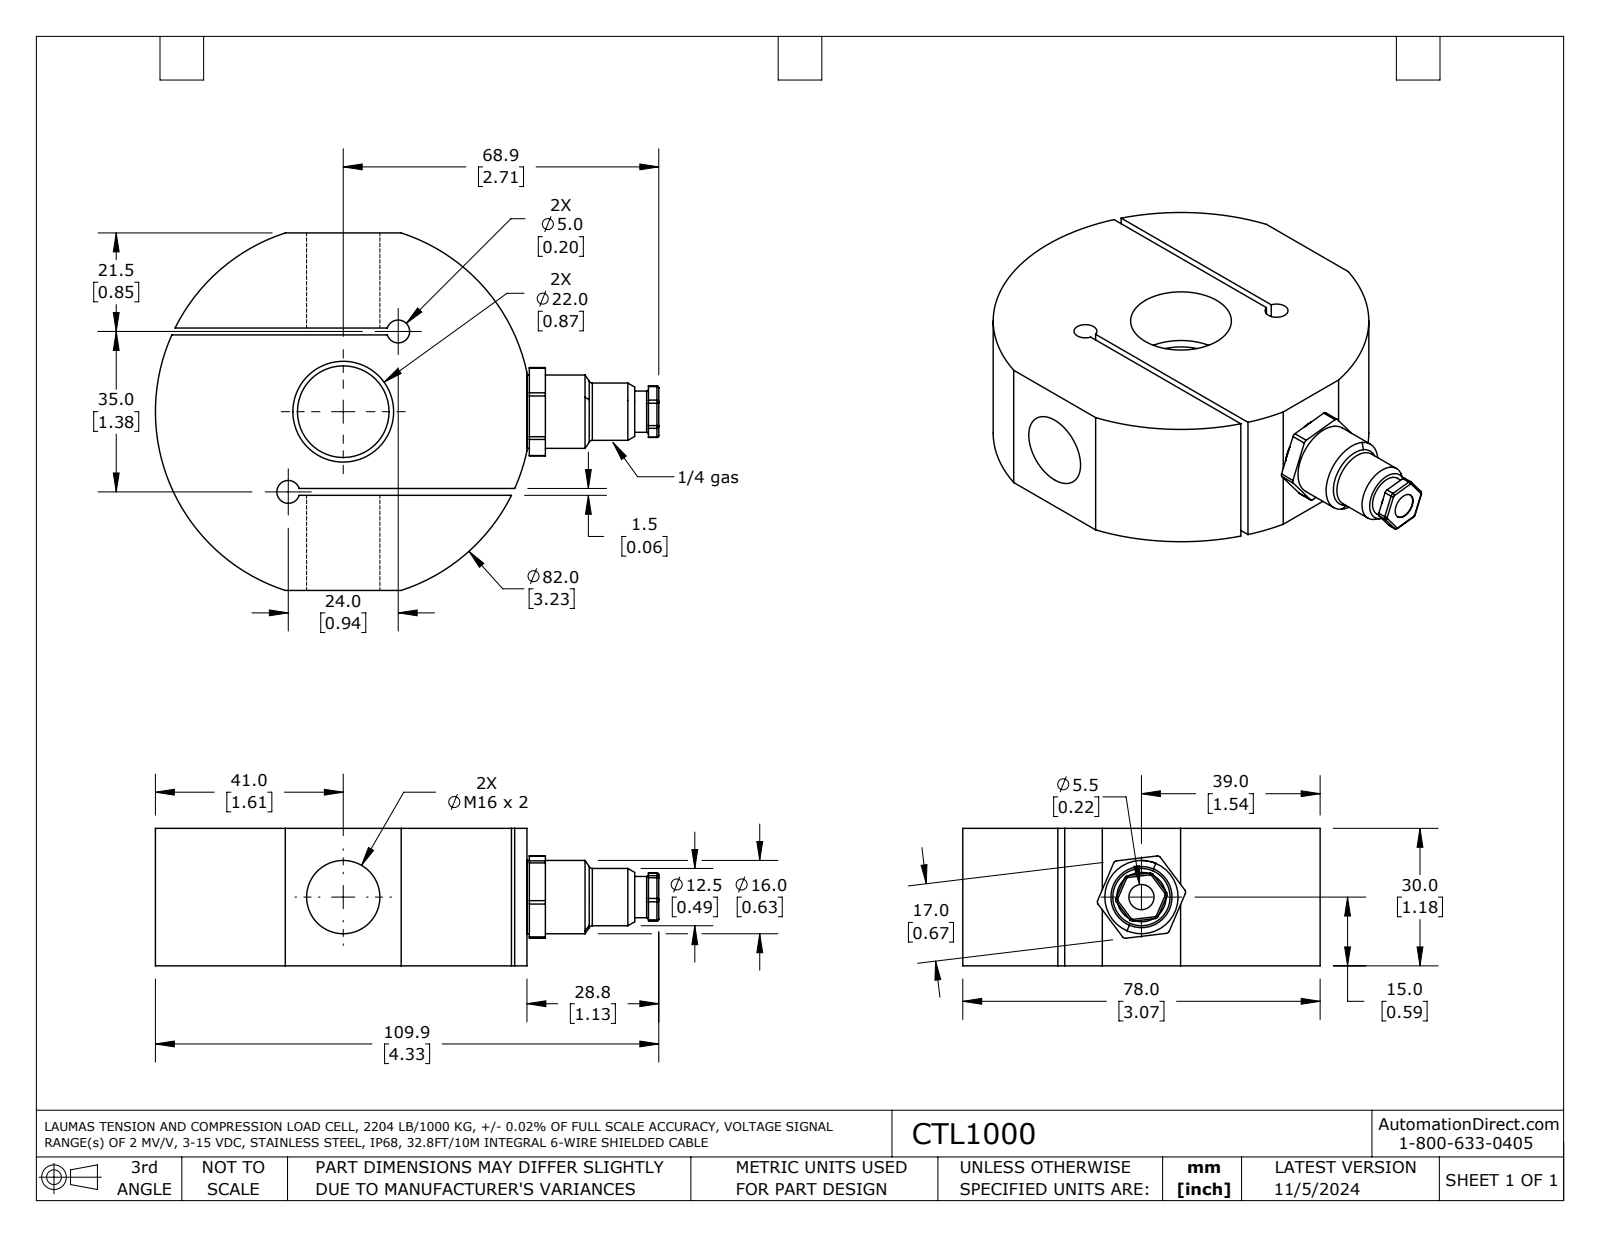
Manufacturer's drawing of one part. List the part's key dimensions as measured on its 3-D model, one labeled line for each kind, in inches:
Part name (STEP PRODUCT): CTL1000
STEP written by: SolidWorks 2021 (AUTOMOTIVE_DESIGN)
Units: inches
Bodies: 2 solids, 102 faces (32 planar, 51 cylindrical, 19 other)
Overall size (bounding box): 4.326 × 3.071 × 1.181
Volume: 8.181 in³ · Surface area: 45.86 in²
Round holes (diameter × count): ⌀0.197 ×2, ⌀0.217 ×1, ⌀0.551 ×1, ⌀0.63 ×1, ⌀0.866 ×1
Round bosses / shafts (diameter × count): ⌀0.63 ×1, ⌀0.492 ×1, ⌀0.354 ×1
Partial cylindrical surfaces — rounded edges, fillets, slot ends (radius × count): R0.03 ×12, R0.016 ×6, R1.614 ×1
Main face-to-face distances: 1.181, 0.059, 1.378, 1.319, 1.437, 0.817, 0.876, 2.195, 2.254, 0.551
Hole centre spacings: 0.835, 1.671
